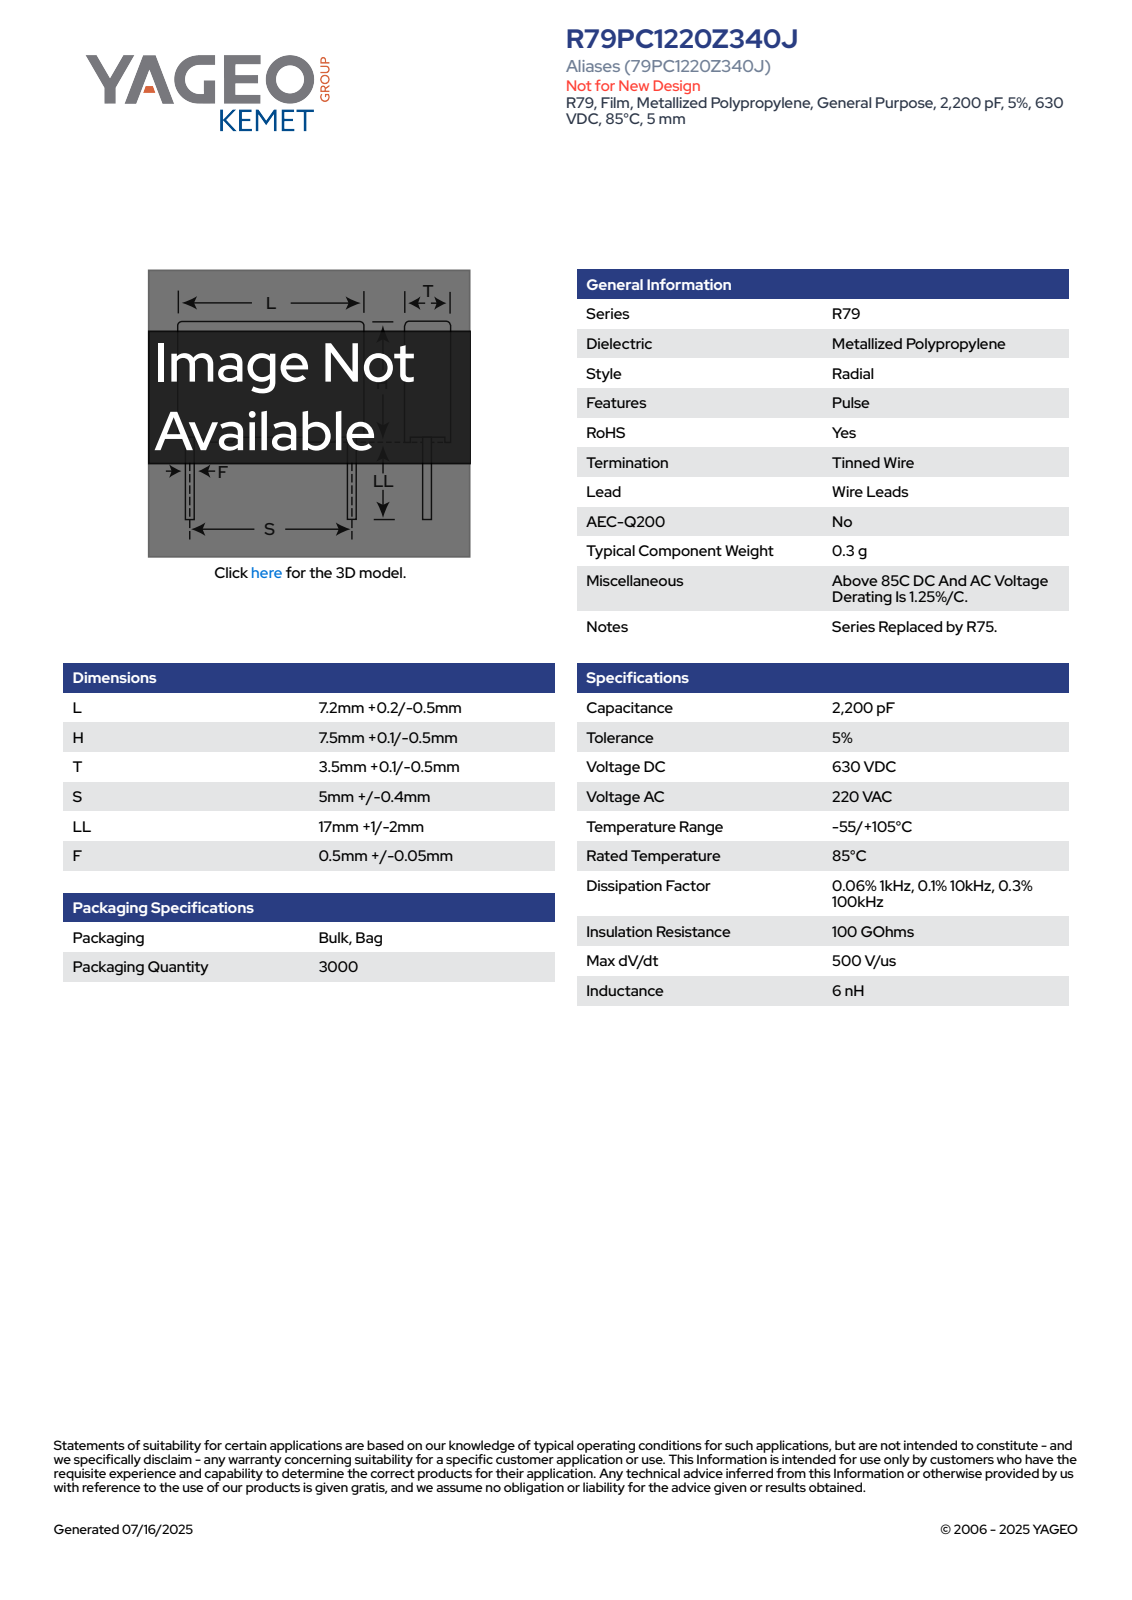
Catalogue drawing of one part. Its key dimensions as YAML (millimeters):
part_name: "CFR_RB2_7.2X7.5X3.5_L7.4H7.6T3.6S5LL18F0.55"
step_written_by: "SolidWorks 2021 (AUTOMOTIVE_DESIGN)"
units: millimeters
bodies: {solids: 4, faces: 85, planar: 77, cylindrical: 8, other: 0}
overall_size: [25.6, 7.4, 3.6]
volume: 194
surface_area: 298
round_bosses_or_shafts:
  - {diameter: 0.55, count: 2}
partial_cylinders:
  - {radius: 0.5, count: 4}
face_to_face_distances: [3.6, 7.4, 6.85, 3.35, 3.1, 7.15, 0.75, 7.6, 6.9, 0.49]
